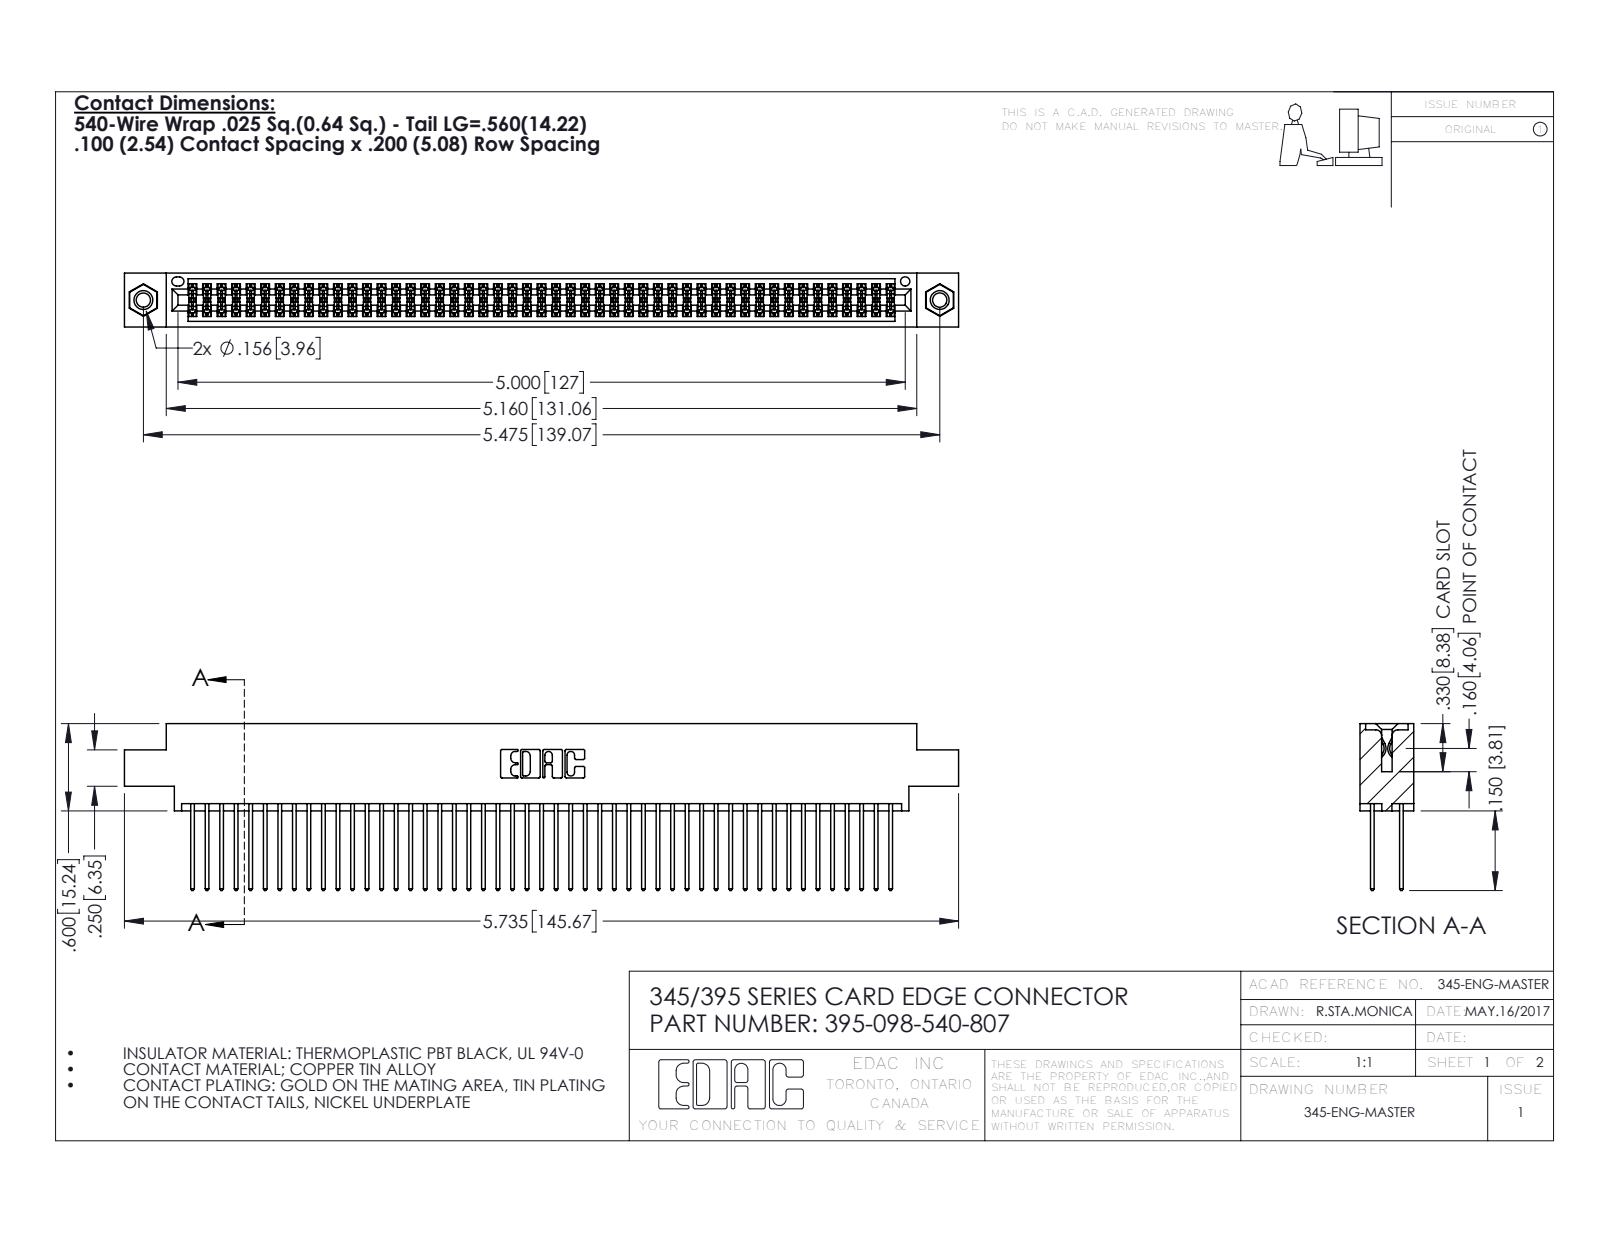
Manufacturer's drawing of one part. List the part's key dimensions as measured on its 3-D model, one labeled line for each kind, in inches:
Part name (STEP PRODUCT): 345-292-001_345-293-140; 395-098-540-807; 345-250-001_345-250-005-103; 345 Part_0.170 Offset - 0.156 Dia-TI
STEP written by: SolidWorks 2016 (CONFIG_CONTROL_DESIGN)
Units: inches
Bodies: 101 solids, 5090 faces (3350 planar, 1724 cylindrical, 16 other)
Overall size (bounding box): 5.735 × 1.147 × 0.37
Volume: 0.882 in³ · Surface area: 36.28 in²
Round holes (diameter × count): ⌀0.098 ×2, ⌀0.125 ×2, ⌀0.156 ×2, ⌀0.064 ×1
Round bosses / shafts (diameter × count): ⌀0.155 ×2
Partial cylindrical surfaces — rounded edges, fillets, slot ends (radius × count): R0.006 ×147, R0.01 ×98, R0.01 ×22, R0.007 ×6, R0.031 ×6, R0.026 ×3, R0.014 ×2, R0.019 ×2
Main face-to-face distances: 0.072, 0.298, 0.2, 0.098, 0.272, 0.025, 0.37, 0.225, 0.175, 0.149
Hole centre spacings: 0.27, 5.239, 5.475
